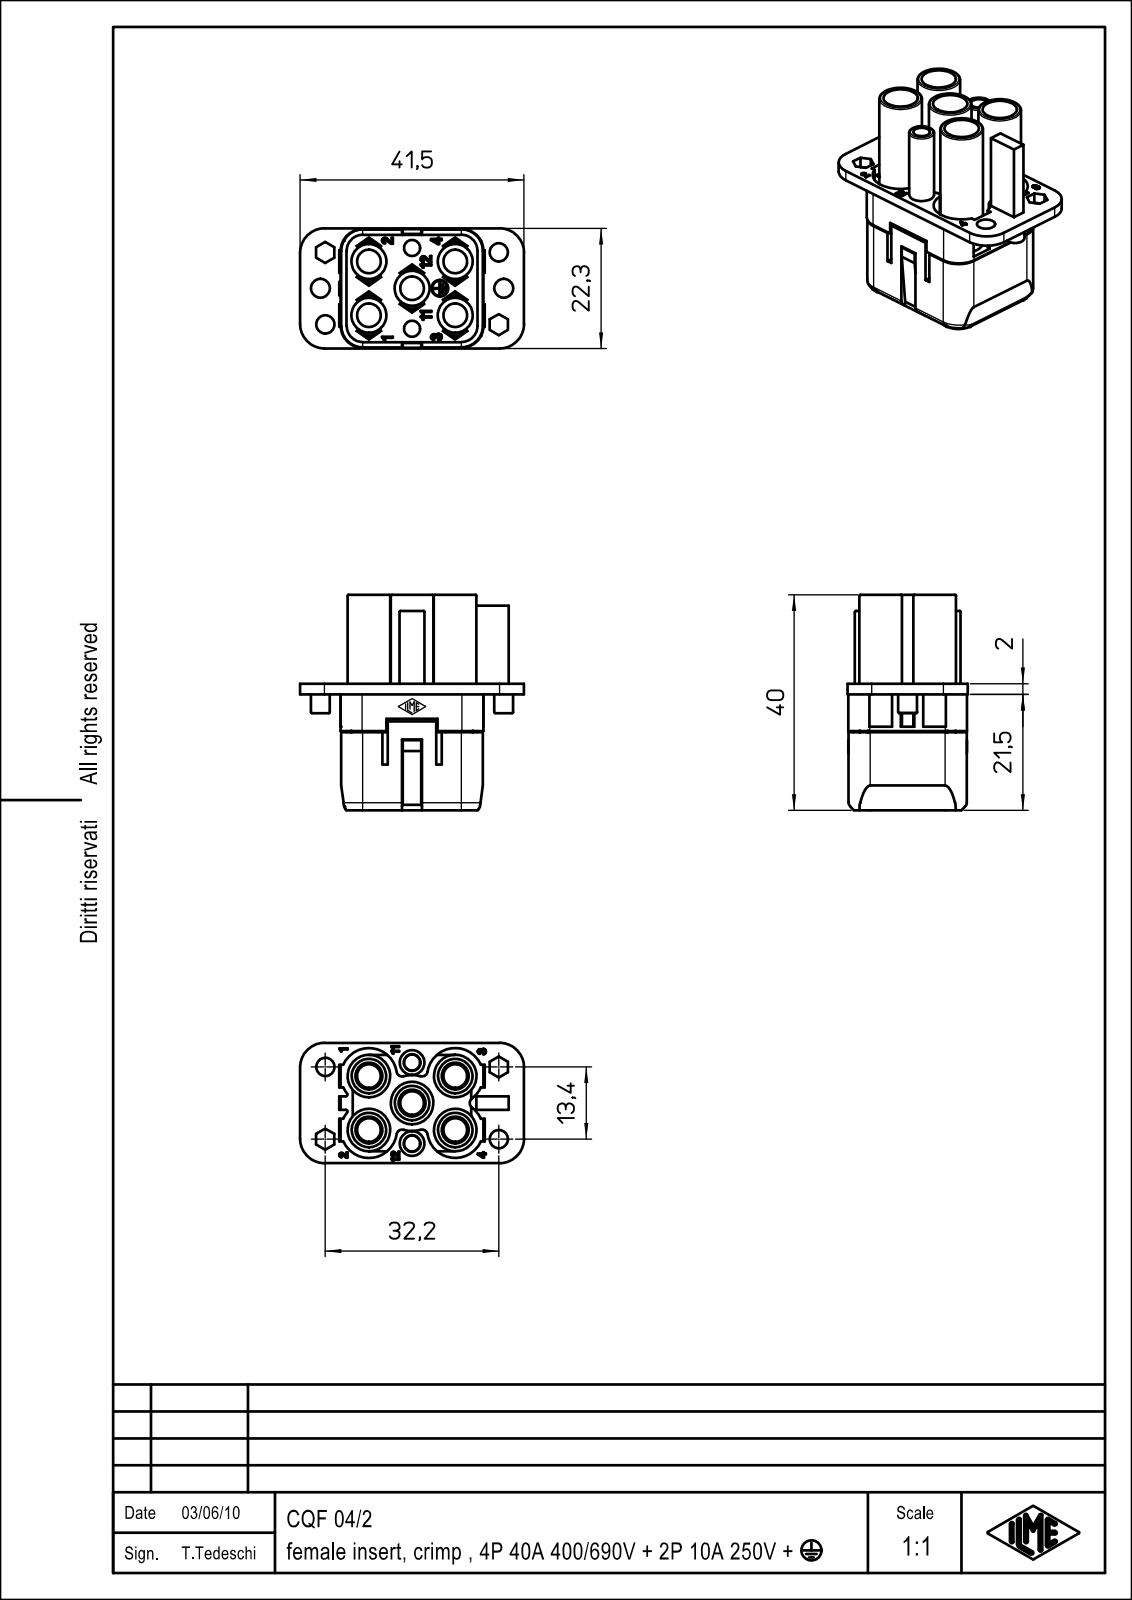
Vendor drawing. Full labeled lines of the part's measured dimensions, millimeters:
Part name (STEP PRODUCT): CQF_04-2
STEP written by: OneSpace Modeling 15.50B 03-Nov-2007 (C) CoCreate Software GmbH (AUTOMOTIVE_DESIGN)
Units: millimetres
Bodies: 1 solid, 843 faces (662 planar, 125 cylindrical, 56 other)
Overall size (bounding box): 41.5 × 40 × 22.3
Volume: 12 891 mm³ · Surface area: 12 261 mm²
Round holes (diameter × count): ⌀4.4 ×5, ⌀6.4 ×5, ⌀6.5 ×5, ⌀3.4 ×2, ⌀3.12 ×1
Round bosses / shafts (diameter × count): ⌀7.9 ×5, ⌀4.6 ×2, ⌀3.5 ×2, ⌀2.83 ×1
Partial cylindrical surfaces — rounded edges, fillets, slot ends (radius × count): R0.1 ×14, R4 ×8, R1 ×7, R5.2 ×5, R2 ×4, R4.5 ×4, R5.1 ×4, R0.3 ×2
Main face-to-face distances: 14.5, 2, 21.5, 1, 23.5, 9, 21.91, 7, 9.75, 12.25
Hole centre spacings: 9.43, 5.56, 8.28, 10, 14.23, 14.45, 16, 17.44
